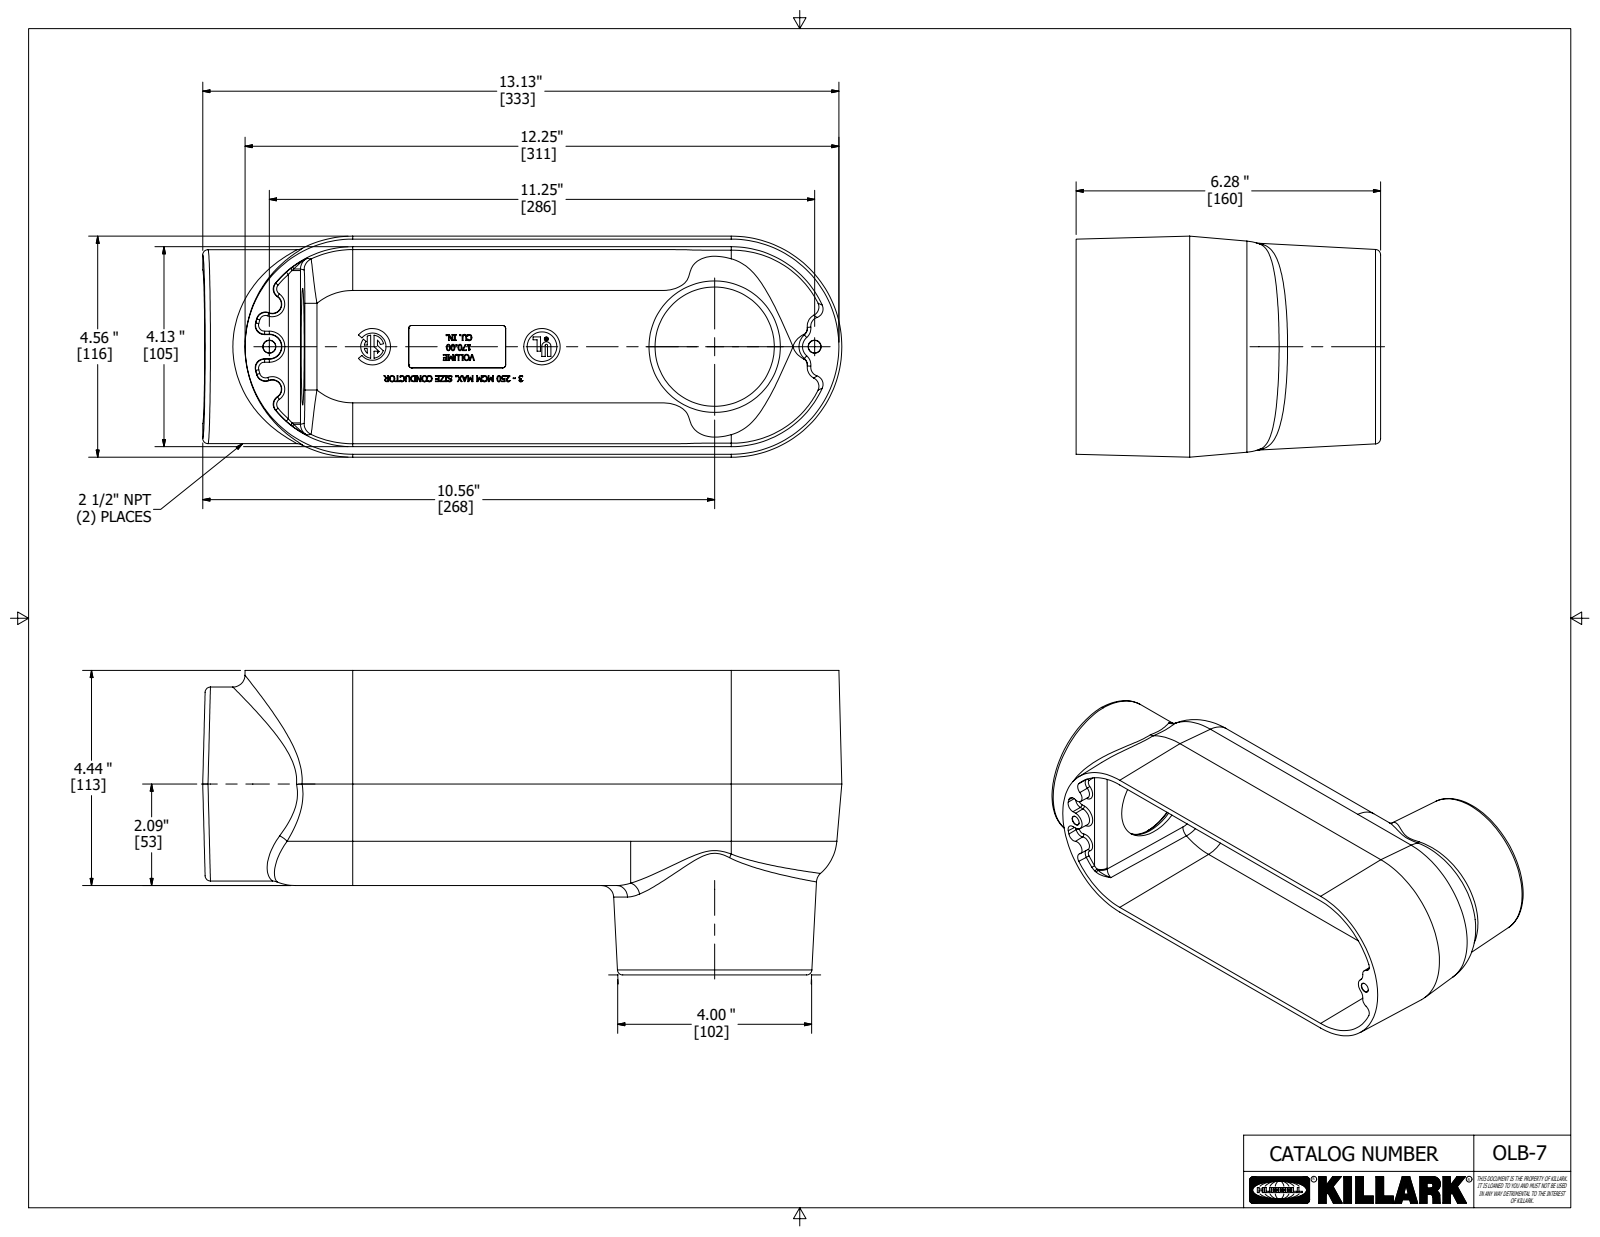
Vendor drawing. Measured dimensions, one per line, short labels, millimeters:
name: 17325-1
written by: Autodesk Inventor 2018 (AUTOMOTIVE_DESIGN)
unit: mm
bodies: 1 solid, 944 faces (529 planar, 39 cylindrical, 376 other)
size: 334.9 × 159.5 × 115.8
volume: 960 400 mm³; area: 244 800 mm²
holes: 2× ⌀6.6, 1× ⌀1.8, 1× ⌀15.5
bosses: 1× ⌀101.6, 1× ⌀19.1, 1× ⌀2.1
rounds: 10× R1.6, 2× R6.4, 2× R25.4, 1× R0.2, 1× R0.3, 1× R0.6, 1× R2.4, 1× R4.3
face distances: 4, 112.7, 108.7, 46.8, 50.8, 159.5, 0.4, 4.3, 51.2, 108.4
hole spacings: 142.9, 4.6, 140.6, 145.2, 285.8
